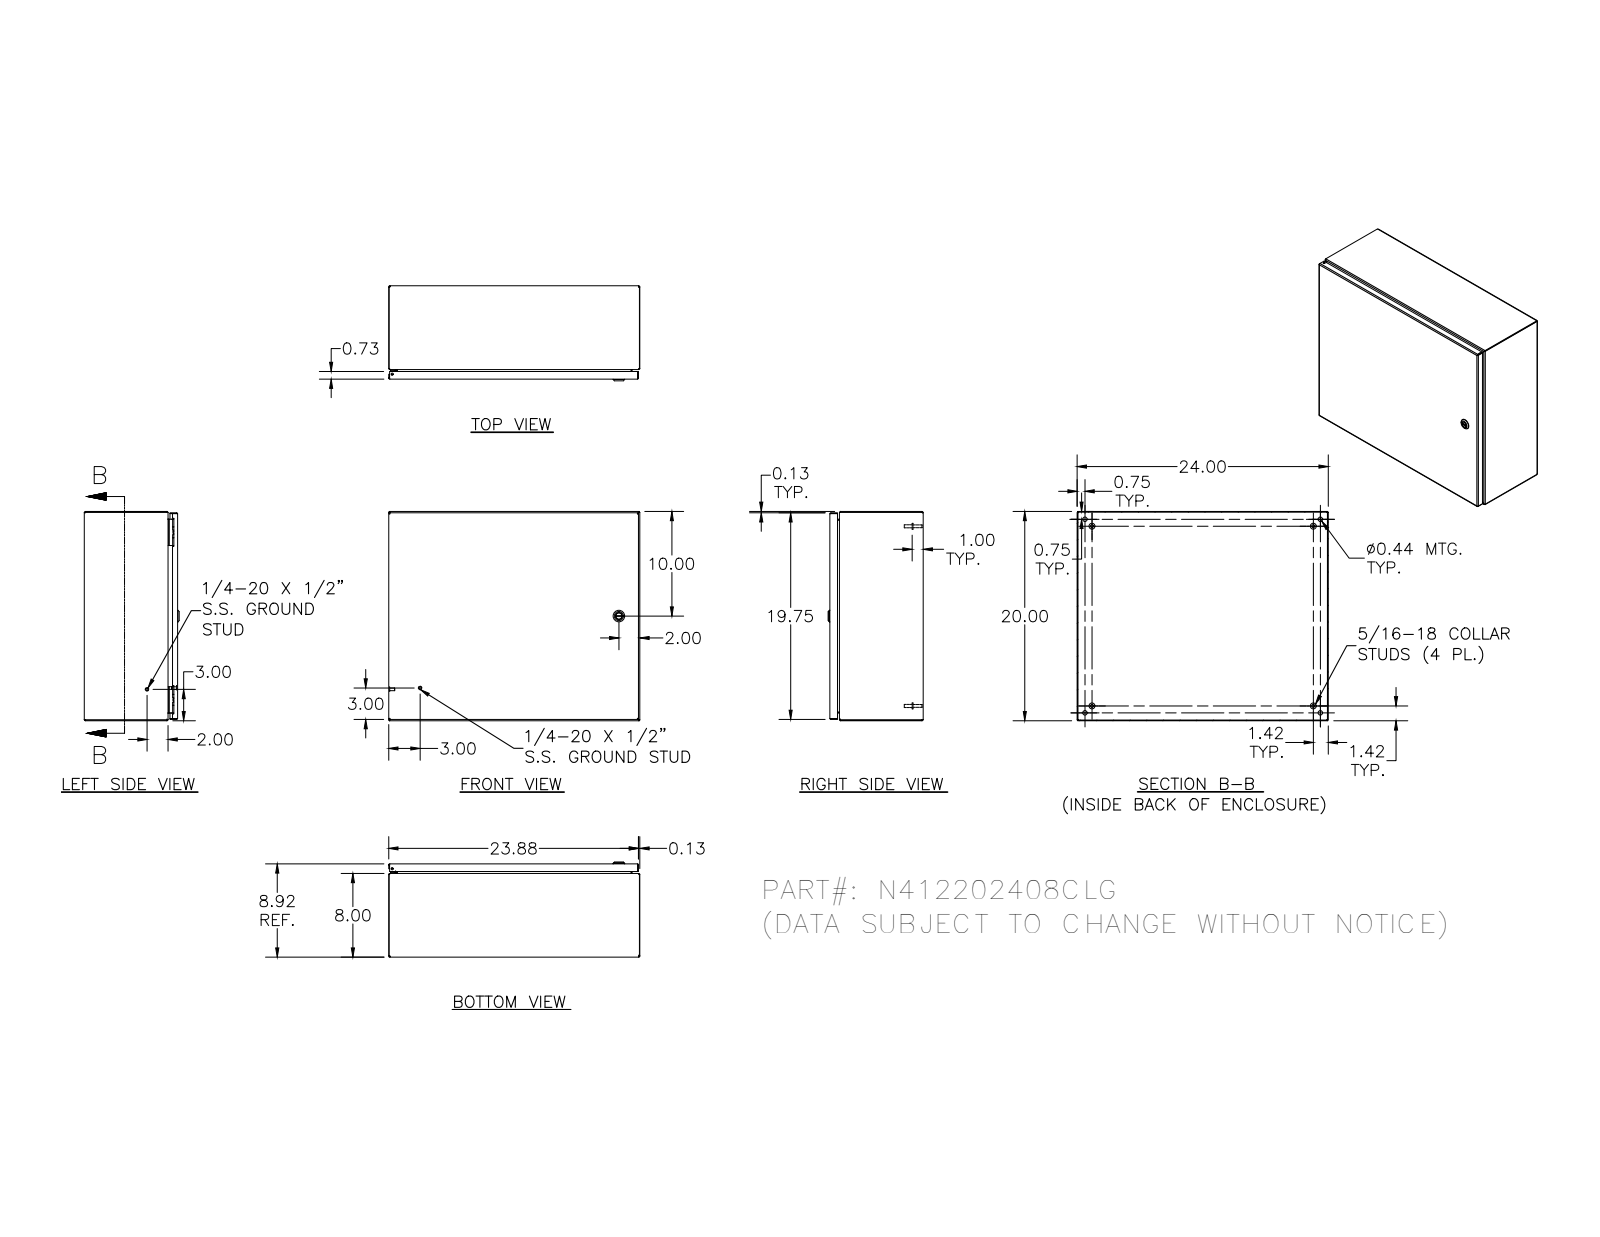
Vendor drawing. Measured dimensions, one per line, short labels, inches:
name: N412202408CLG
written by: SolidWorks 2018 (AUTOMOTIVE_DESIGN)
unit: in
bodies: 33 solids, 1449 faces (530 planar, 547 cylindrical, 372 other)
size: 24 × 20 × 9.075
volume: 136.2 in³; area: 3 703 in²
holes: 5× ⌀0.188, 4× ⌀0.093, 4× ⌀0.152, 4× ⌀0.167, 4× ⌀0.172, 4× ⌀0.437, 2× ⌀0.156, 1× ⌀0.187, 1× ⌀0.197, 1× ⌀0.315, 1× ⌀0.394, 1× ⌀0.402
bosses: 10× ⌀0.25, 4× ⌀0.563, 4× ⌀0.36, 4× ⌀0.32, 4× ⌀0.3, 4× ⌀0.275, 4× ⌀0.256, 4× ⌀0.164
rounds: 30× R0.012, 30× R0.031, 26× R0.05, 20× R0.105, 18× R0.016, 16× R0.125, 13× R0.02, 8× R0.032
face distances: 0.074, 8.843, 8.769, 8.917, 0.074, 19.926, 20, 19.852, 19.926, 23.926
hole spacings: 16, 0.66, 0.656, 1.307, 1.965, 15.34, 16.66, 0.5
